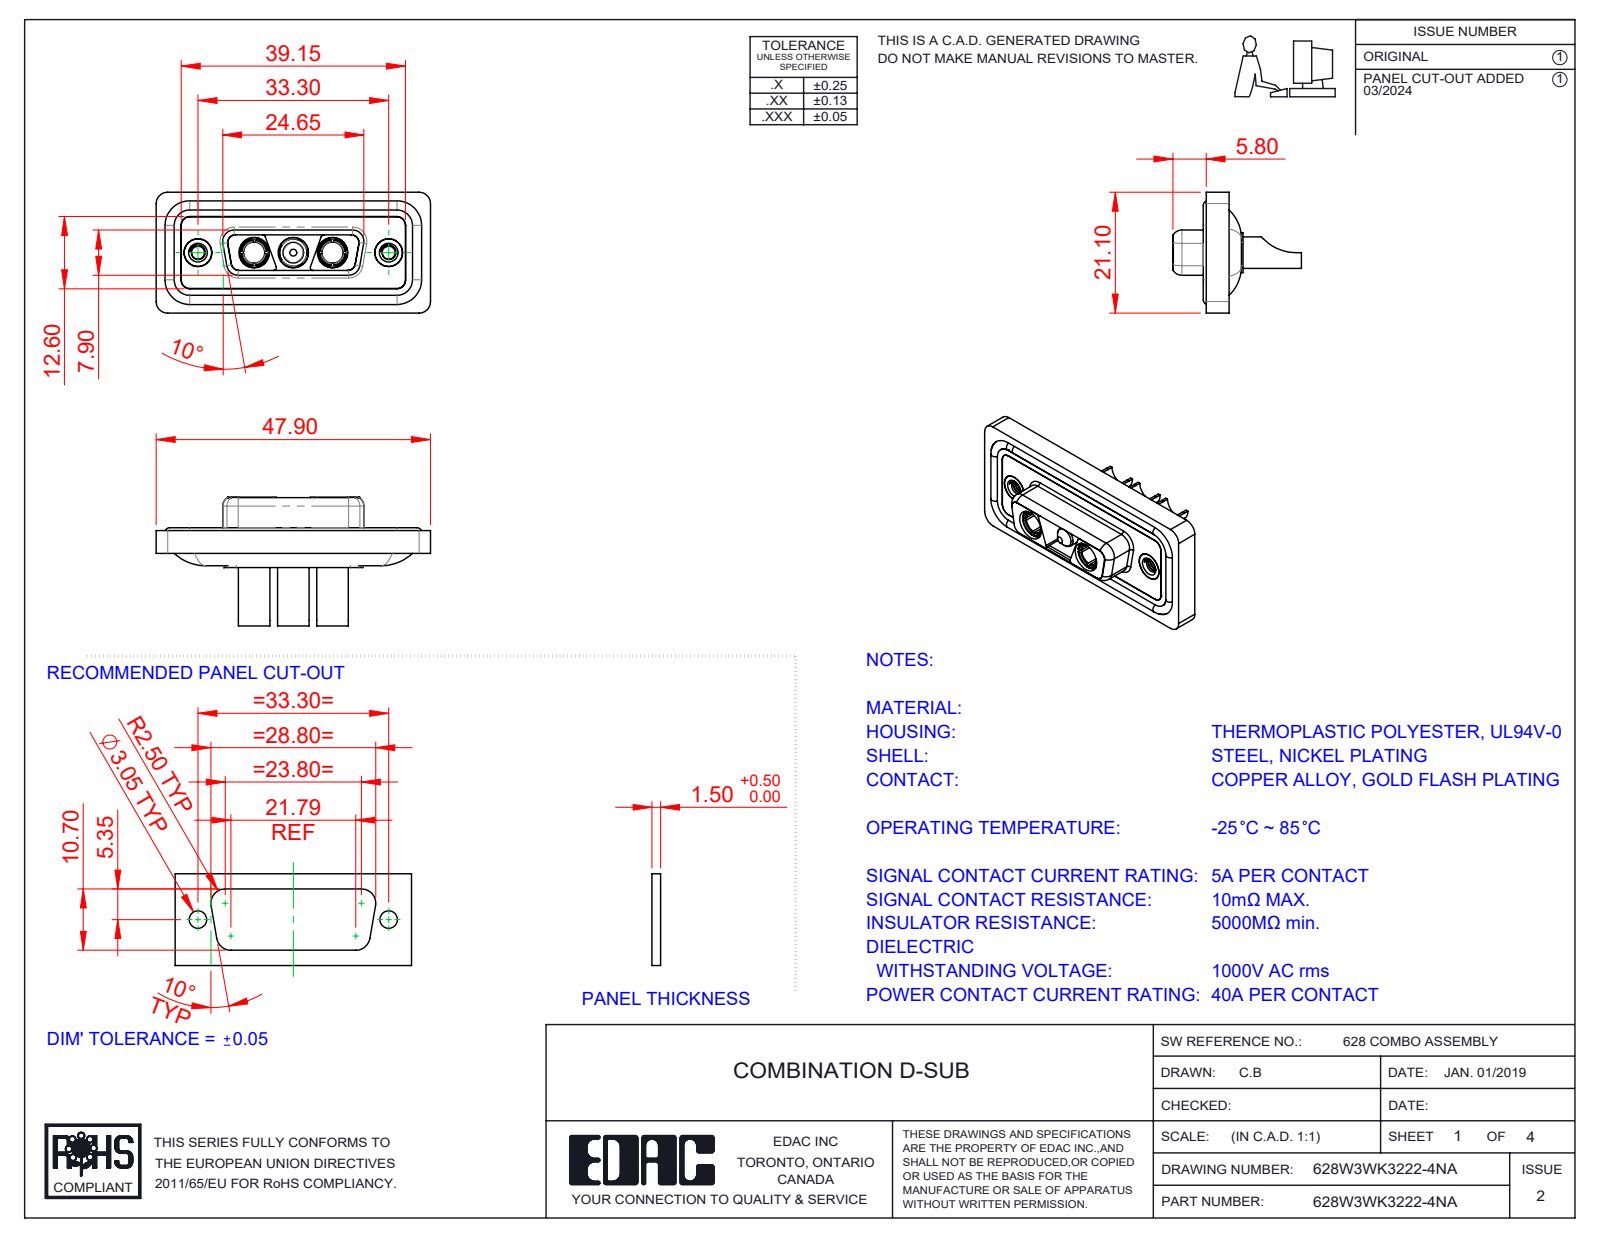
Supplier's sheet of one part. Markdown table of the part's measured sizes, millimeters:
| quantity | value |
| --- | --- |
| part name | Power Socket_40A SC; 628Combo Waterproof Housing_15 Contacts; Power Pin_40A SC; 628Combo Shell Front_15 Contacts (+4 more) |
| STEP written by | SolidWorks 2023 (CONFIG_CONTROL_DESIGN) |
| units | millimeters |
| bodies | 13 solids, 591 faces (184 planar, 263 cylindrical, 144 other) |
| overall size | 47.9 × 22.45 × 21.1 |
| volume | 5 999 mm³ |
| surface area | 9 922 mm² |
| round holes (diameter × count) | 4.85 × 5, 4.6 × 3, 5.3 × 3, 2.26 × 2, 3.7 × 2, 4 × 2, 4.05 × 2, 5 × 2 |
| round bosses / shafts (diameter × count) | 1.6 × 4, 5.5 × 3, 5.2 × 3, 4.75 × 3, 3.75 × 3, 4.96 × 2, 4.95 × 2, 4.8 × 2 |
| partial cylindrical surfaces (radius × count) | 1.5 × 22, 2 × 20, 1.35 × 12, 0.5 × 8, 1.6 × 8, 0.25 × 4, 0.6 × 4, 0.65 × 4 |
| main face-to-face distances | 0.4, 1.6, 0.5, 1.1, 2.9, 5.65, 1.8, 7.05, 5.35, 6.6 |
| hole center spacings | 6.85, 9.8, 16.65, 23.5, 13.7, 33.3 |
